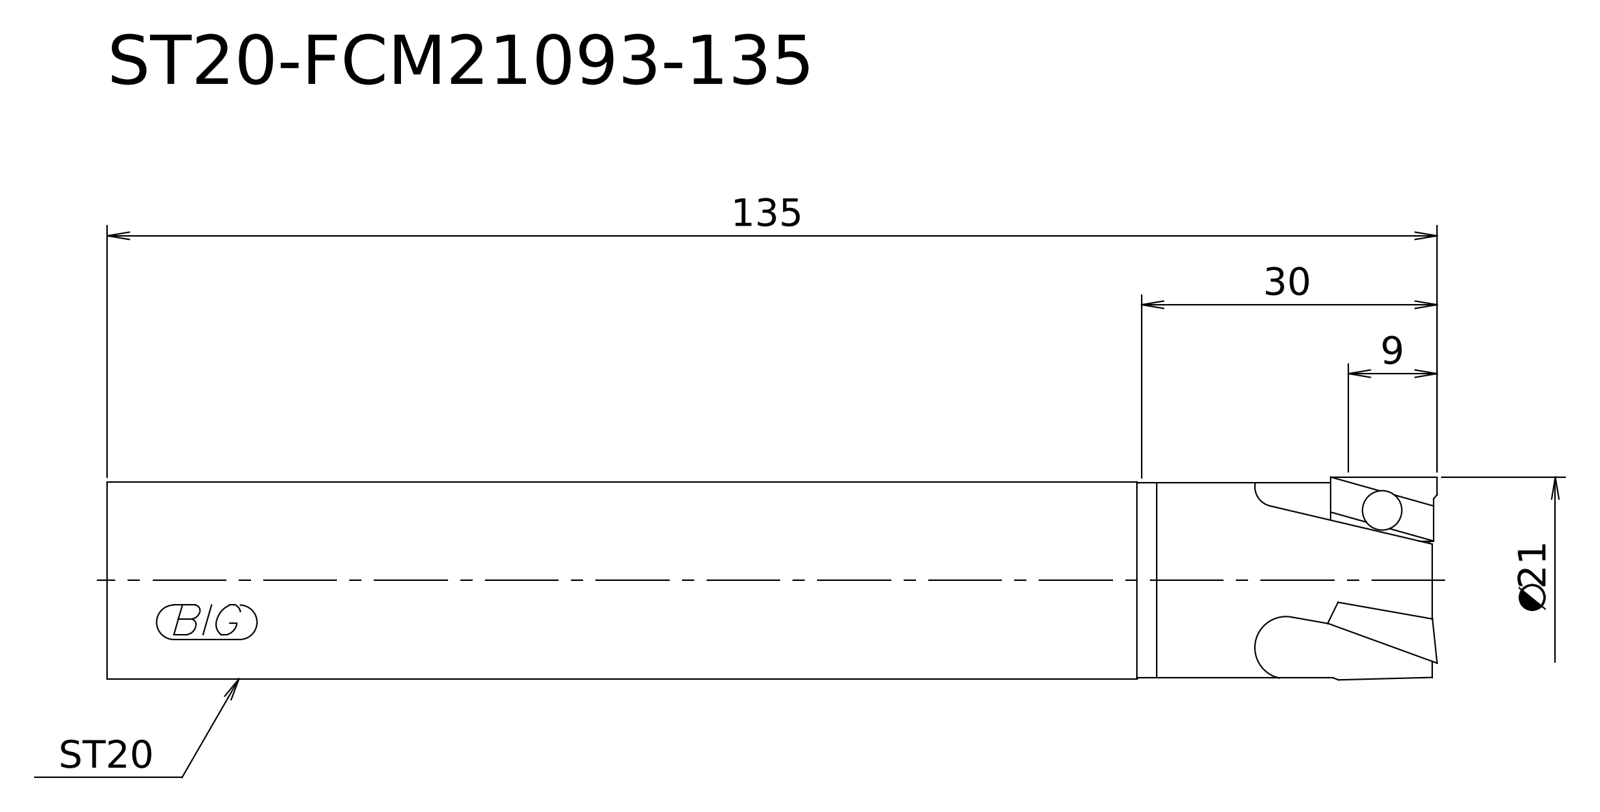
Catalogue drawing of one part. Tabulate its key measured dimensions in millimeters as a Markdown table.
| quantity | value |
| --- | --- |
| STEP written by | Kubotek KeyCreator V8.5.1 (14335) (CONFIG_CONTROL_DESIGN) |
| units | millimeters |
| bodies | 1 solid, 7 faces (3 planar, 3 cylindrical, 1 other) |
| overall size | 135 × 21 × 21 |
| volume | 42 637 mm³ |
| surface area | 9 205 mm² |
| round bosses / shafts (diameter × count) | 21 × 1, 20 × 1, 19.8 × 1 |
| main face-to-face distances | 135, 10.81, 124.19 |
